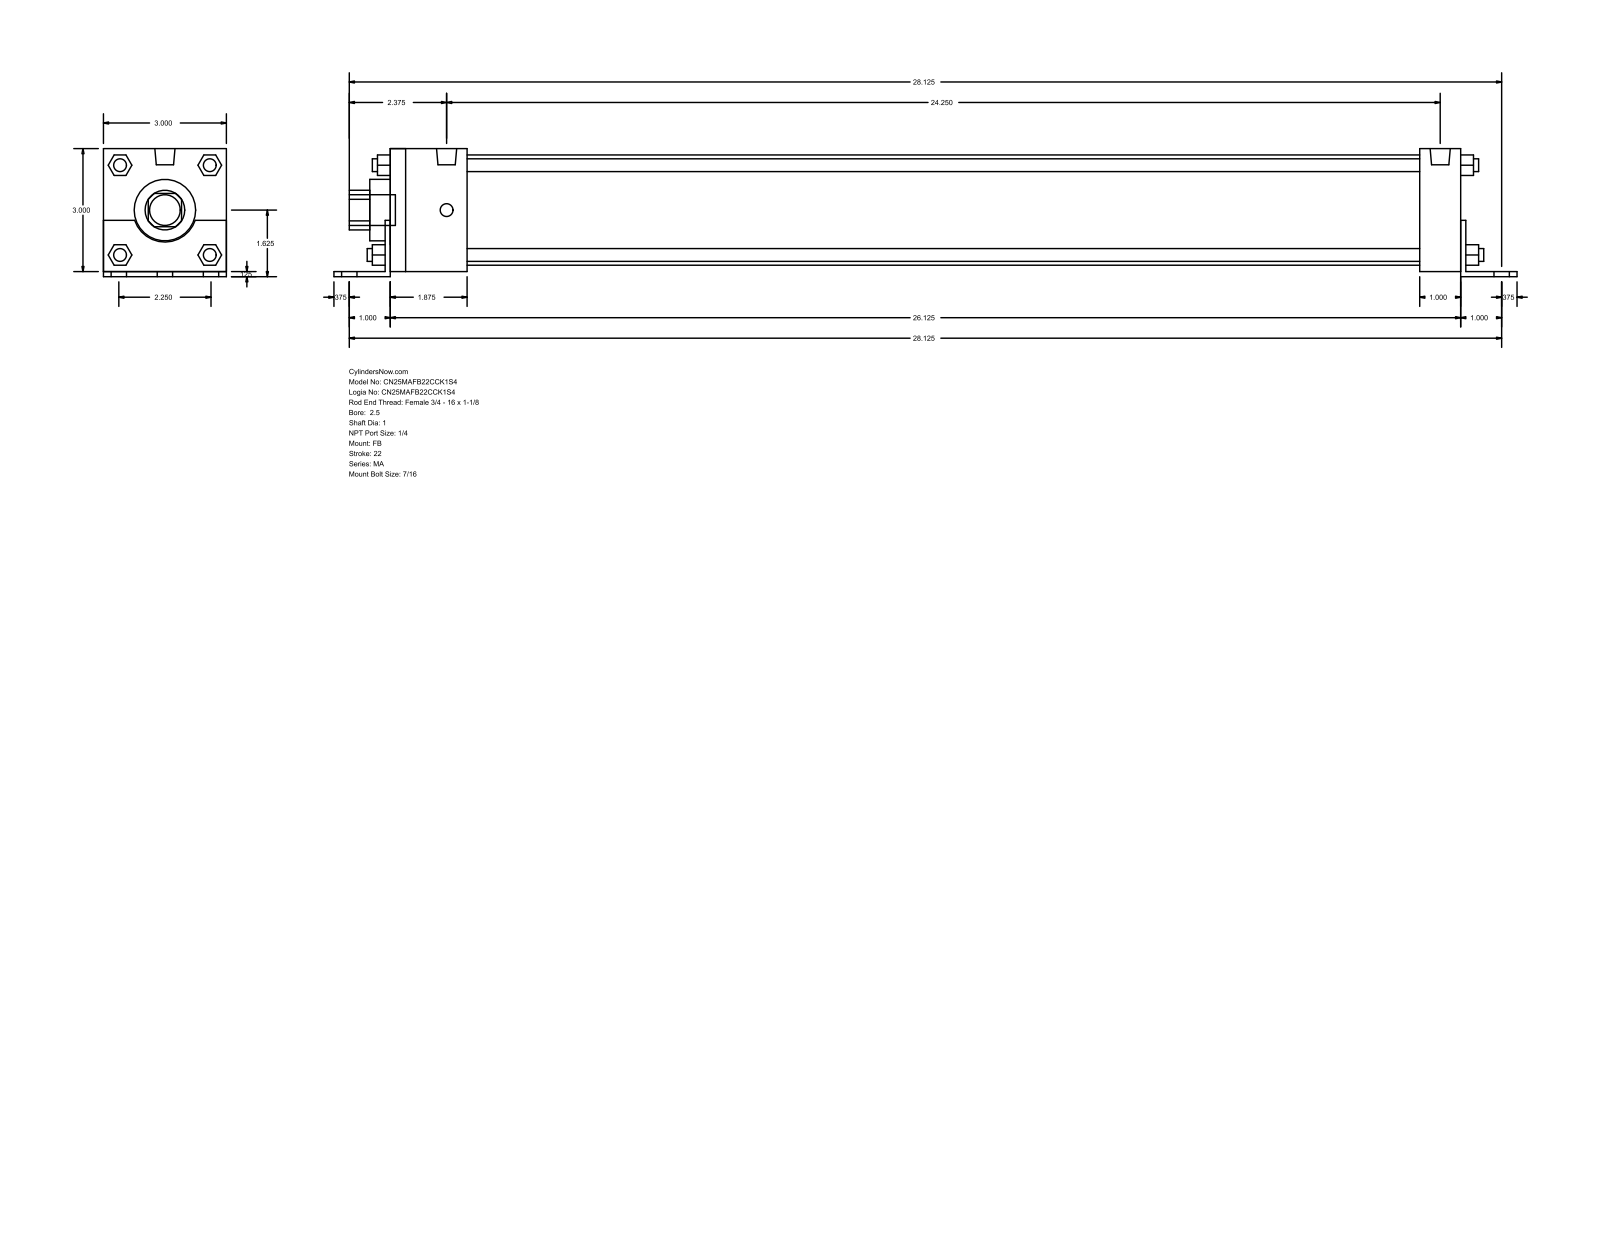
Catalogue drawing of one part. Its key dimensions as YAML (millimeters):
part_name: "MA_FB__0250_1"
step_written_by: "GSSL Pune (CONFIG_CONTROL_DESIGN)"
units: millimeters
bodies: {solids: 0, faces: 140, planar: 105, cylindrical: 35, other: 0}
overall_size: [733.42, 79.38, 76.2]
round_holes:
  - {diameter: 25.4, count: 1}
  - {diameter: 38.1, count: 1}
  - {diameter: 68.33, count: 1}
round_bosses_or_shafts:
  - {diameter: 7.94, count: 8}
  - {diameter: 11.11, count: 6}
  - {diameter: 12.49, count: 2}
  - {diameter: 19.05, count: 1}
partial_cylinders:
  - {radius: 12.29, count: 1}
  - {radius: 19.81, count: 1}
face_to_face_distances: [76.2, 3.17, 79.37, 666.75, 663.58, 12.7, 25.4, 28.57, 47.63, 615.95]
